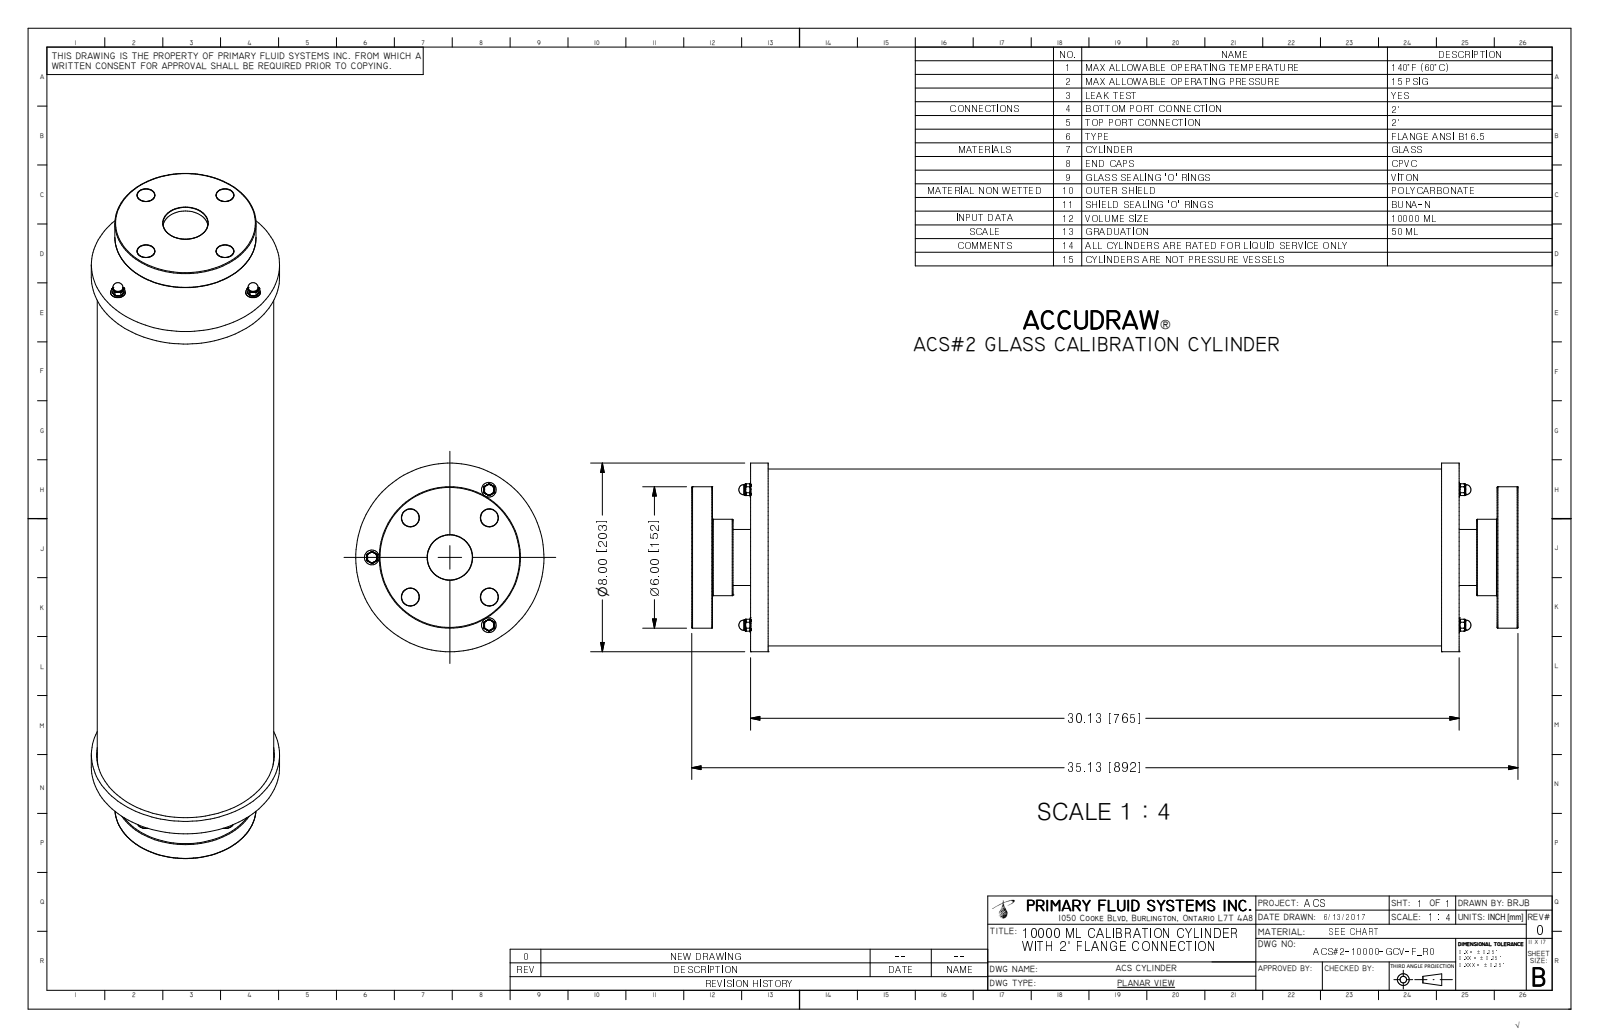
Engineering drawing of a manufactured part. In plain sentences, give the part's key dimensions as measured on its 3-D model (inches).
The part is named "ACS#2-10000-GCV-F_R0". Its 3-D file was written by "Autodesk Inventor 2009 (AUTOMOTIVE_DESIGN)". It is 1 solid with 201 faces: 22 planar, 27 cylindrical and 152 other. Overall it measures 35.13 by 8 by 8 inches. Its volume is 1 392 cubic inches and its surface area 1 071 square inches. Round holes: 4 of diameter 0.745, 1 of diameter 1.913, 1 of diameter 1.939. Round bosses or shafts: 3 of diameter 0.625, 1 of diameter 8, 1 of diameter 7.5, 1 of diameter 6, 1 of diameter 3.244, 1 of diameter 2.375. The main face-to-face distances are 2.5, 32.63, 30.13, 0.885, 34.245, 1.615, 31.745, 35.13, 33.36, 29.38. The hole center spacings are 2.375, 3.359, 4.75.
